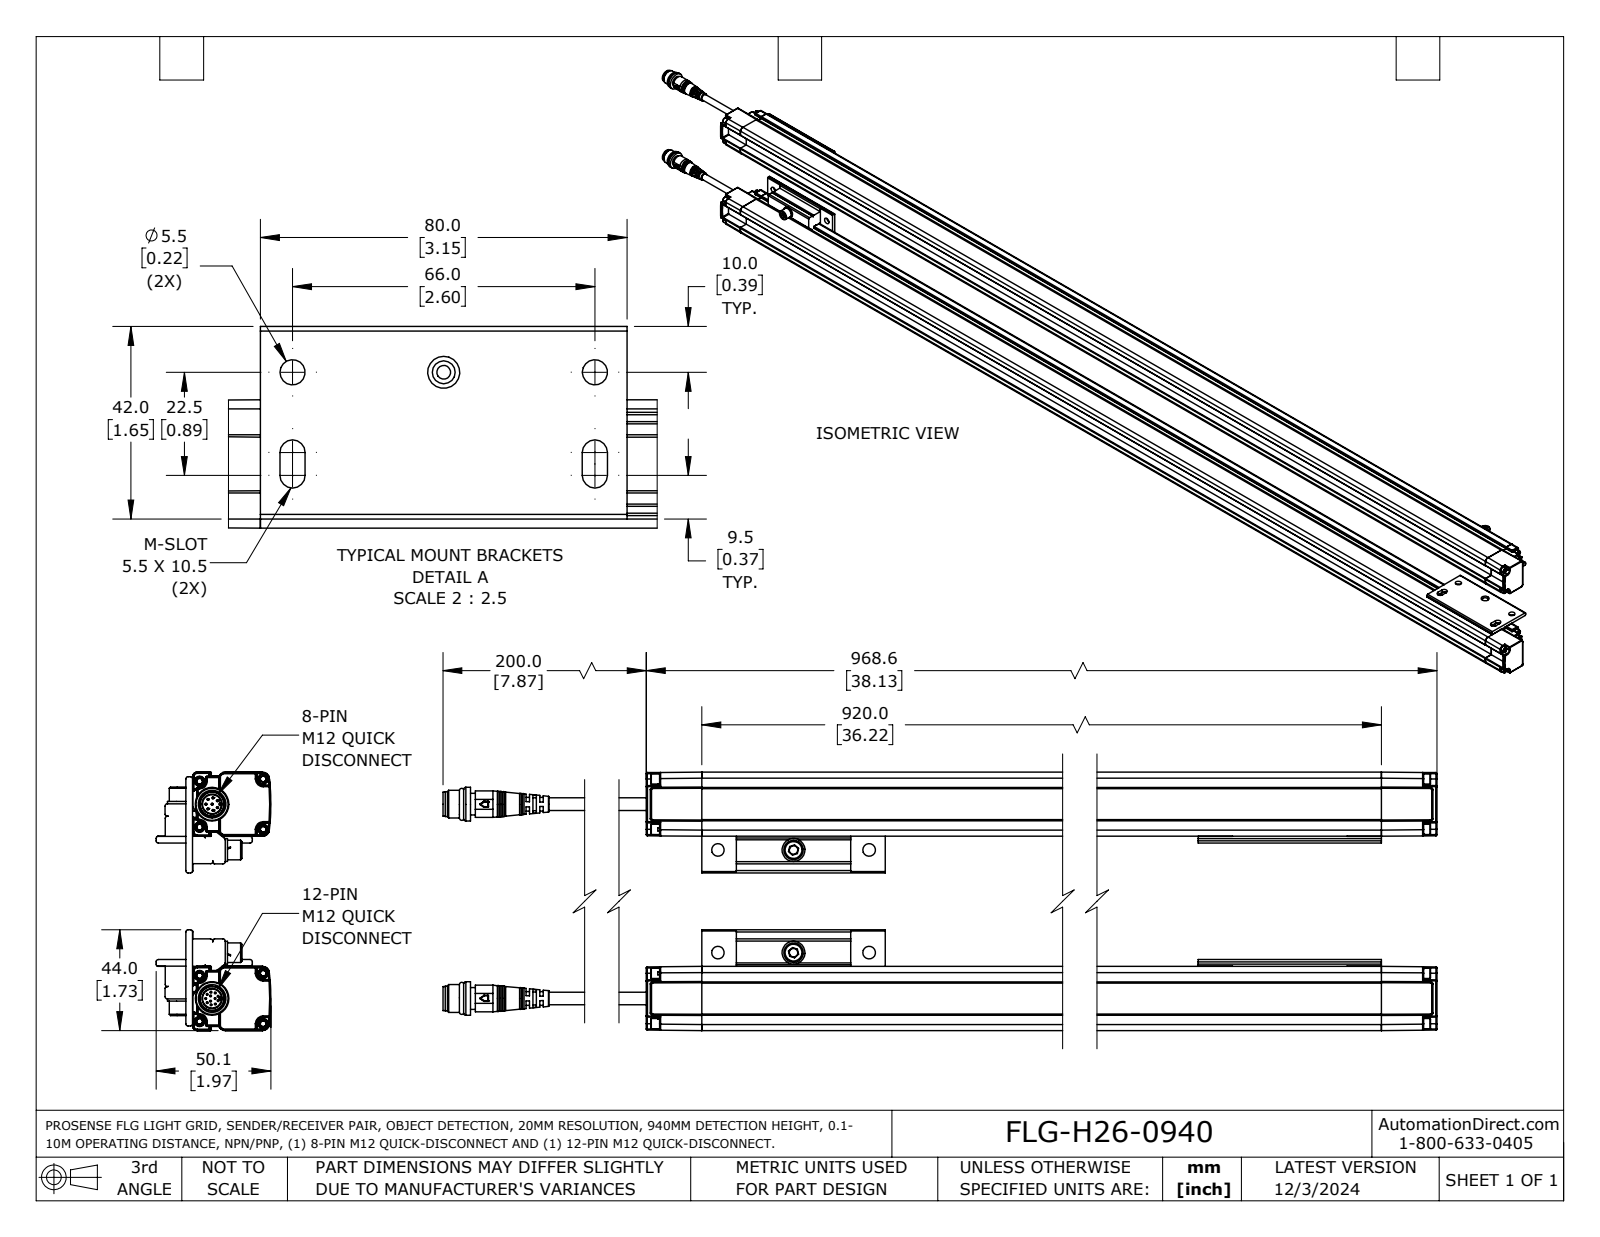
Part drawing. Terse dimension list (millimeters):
name: FLG-H26-0940
written by: SolidWorks 2023 (AUTOMOTIVE_DESIGN)
unit: mm
bodies: 10 solids, 1668 faces (816 planar, 456 cylindrical, 396 other)
size: 1060.55 × 112.8 × 50.09
volume: 1 575 000 mm³; area: 396 948 mm²
holes: 16× ⌀0.4, 6× ⌀5.5, 4× ⌀2.5, 3× ⌀5, 2× ⌀8.3
bosses: 20× ⌀0.8, 8× ⌀4.5, 8× ⌀3, 4× ⌀5.5, 4× ⌀1.5, 3× ⌀10, 3× ⌀8.5, 3× ⌀3.7
rounds: 142× R0.5, 40× R1, 20× R0.25, 12× R0.2, 12× R0.3, 12× R2.75, 6× R2.55, 4× R1.25
face distances: 84.8, 28, 1.8, 7.25, 20.75, 24.65, 56.8, 112.8, 26.45, 5.45
hole spacings: 2.75, 33, 4.15, 24.87, 55.64, 5.45, 44.8, 66
